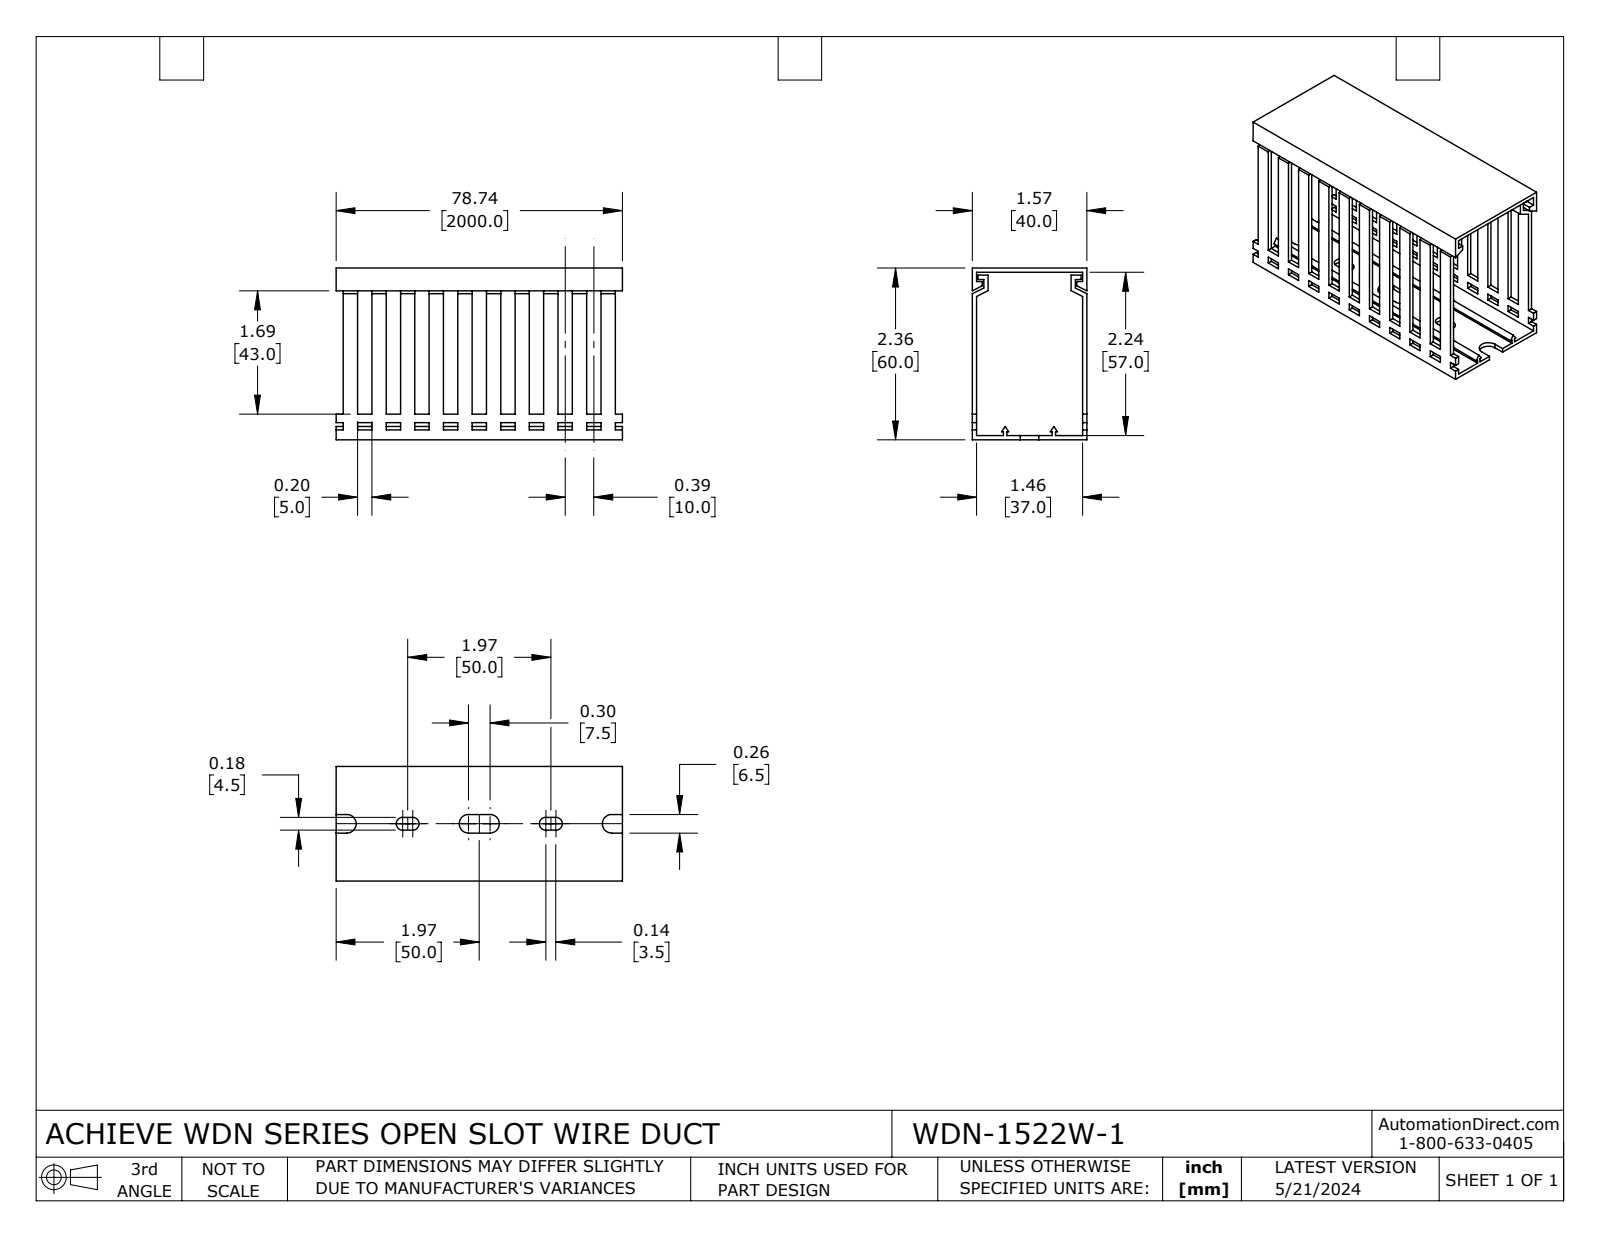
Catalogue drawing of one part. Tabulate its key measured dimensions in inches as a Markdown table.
| quantity | value |
| --- | --- |
| part name | WDN-1522W-1 |
| STEP written by | SolidWorks 2023 (CONFIG_CONTROL_DESIGN) |
| units | inches |
| bodies | 2 solids, 350 faces (338 planar, 12 cylindrical, 0 other) |
| overall size | 3.937 × 2.362 × 1.575 |
| volume | 1.519 in³ |
| surface area | 58.78 in² |
| partial cylindrical surfaces (radius × count) | 0.089 × 4, 0.128 × 4 |
| main face-to-face distances | 0.059, 2.303, 1.516, 1.575, 2.362, 2.244, 0.197, 1.457, 0.394, 0.591 |
